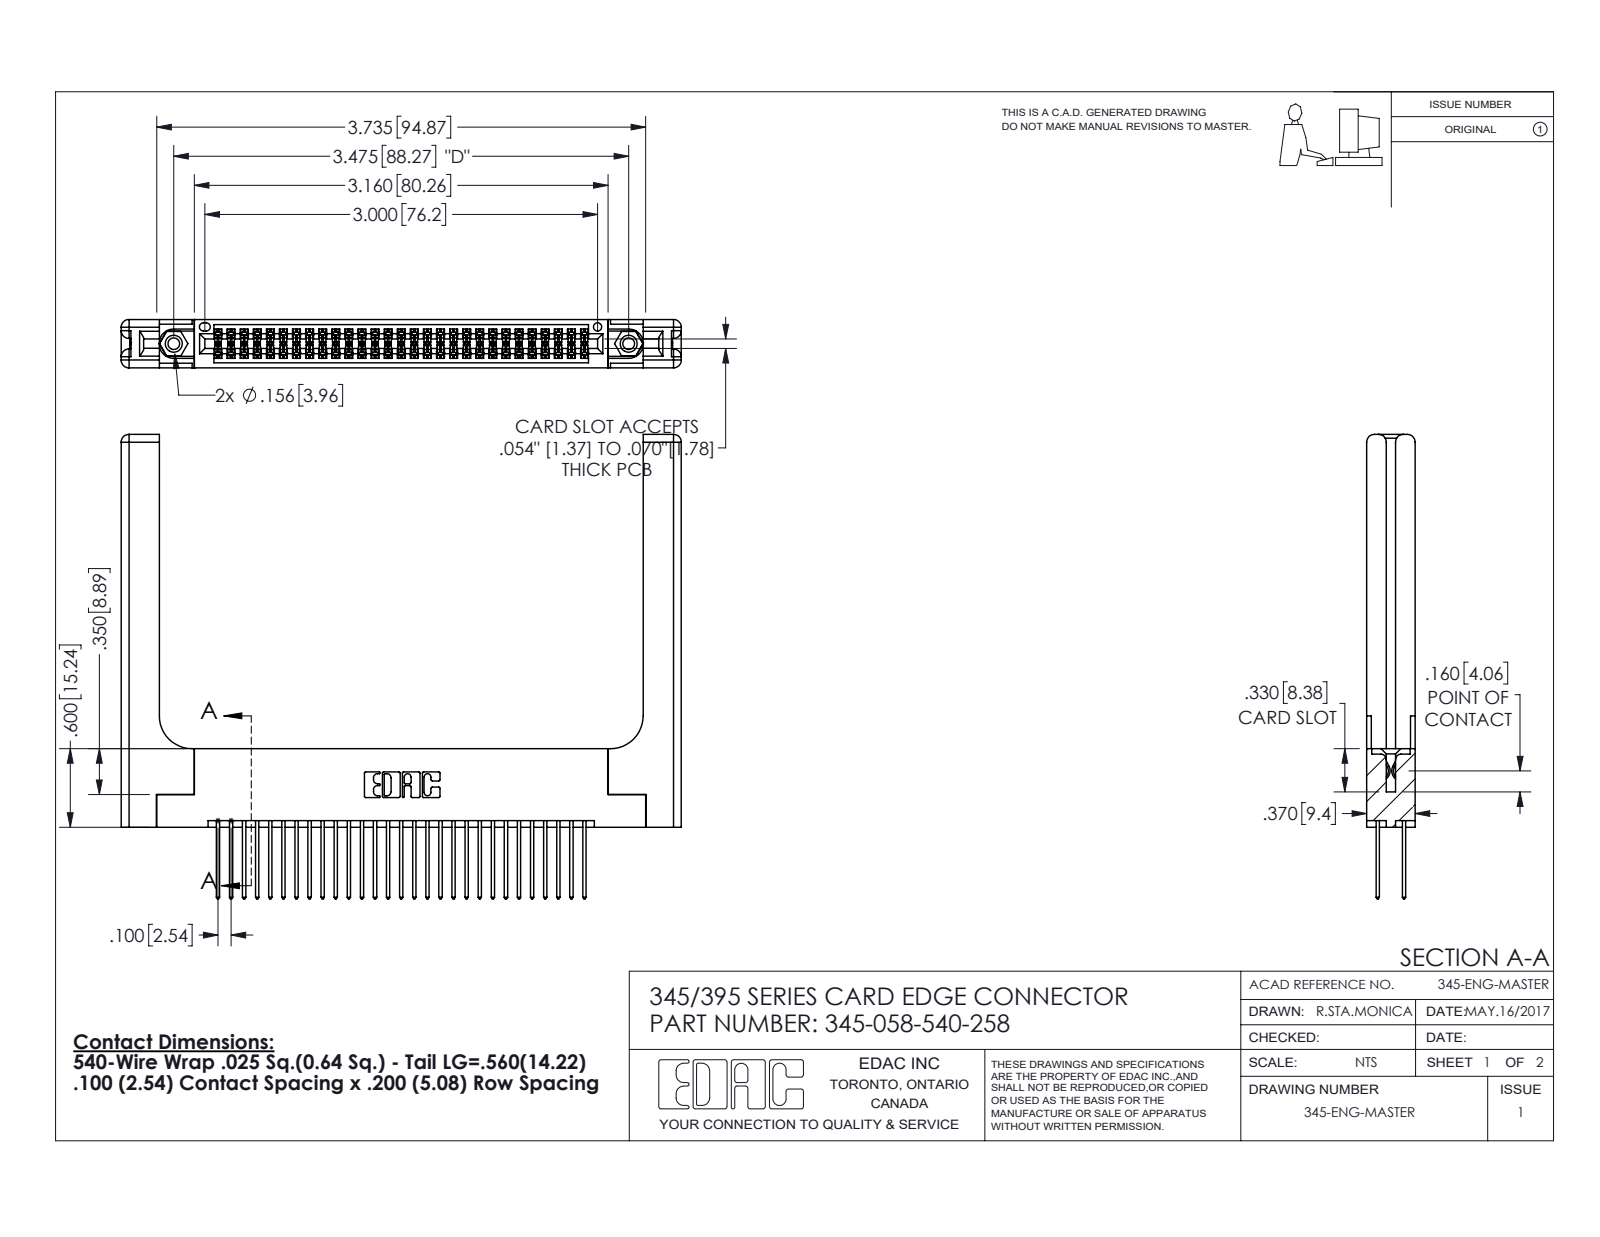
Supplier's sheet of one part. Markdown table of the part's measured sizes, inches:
| quantity | value |
| --- | --- |
| part name | 345-220-058_345-220-058; 345 Part_Flush Mounting Lugs - 0.156 Dia-TH; 345-292-001_345-293-140; 345-250-001_345-250-001-102 (+1 more) |
| STEP written by | SolidWorks 2016 (CONFIG_CONTROL_DESIGN) |
| units | inches |
| bodies | 63 solids, 3282 faces (2142 planar, 1080 cylindrical, 60 other) |
| overall size | 4.279 × 3.547 × 0.37 |
| volume | 1.168 in³ |
| surface area | 33.45 in² |
| round holes (diameter × count) | 0.089 × 2, 0.125 × 2, 0.156 × 2, 0.064 × 1 |
| round bosses / shafts (diameter × count) | 0.155 × 2 |
| partial cylindrical surfaces (radius × count) | 0.006 × 87, 0.01 × 58, 0.01 × 22, 0.06 × 16, 0.007 × 6, 0.031 × 6, 0.026 × 3, 0.014 × 2 |
| main face-to-face distances | 0.072, 0.298, 0.37, 0.2, 0.098, 0.272, 0.025, 0.225, 0.148, 0.15 |
| hole center spacings | 0.27, 3.24, 3.475 |
